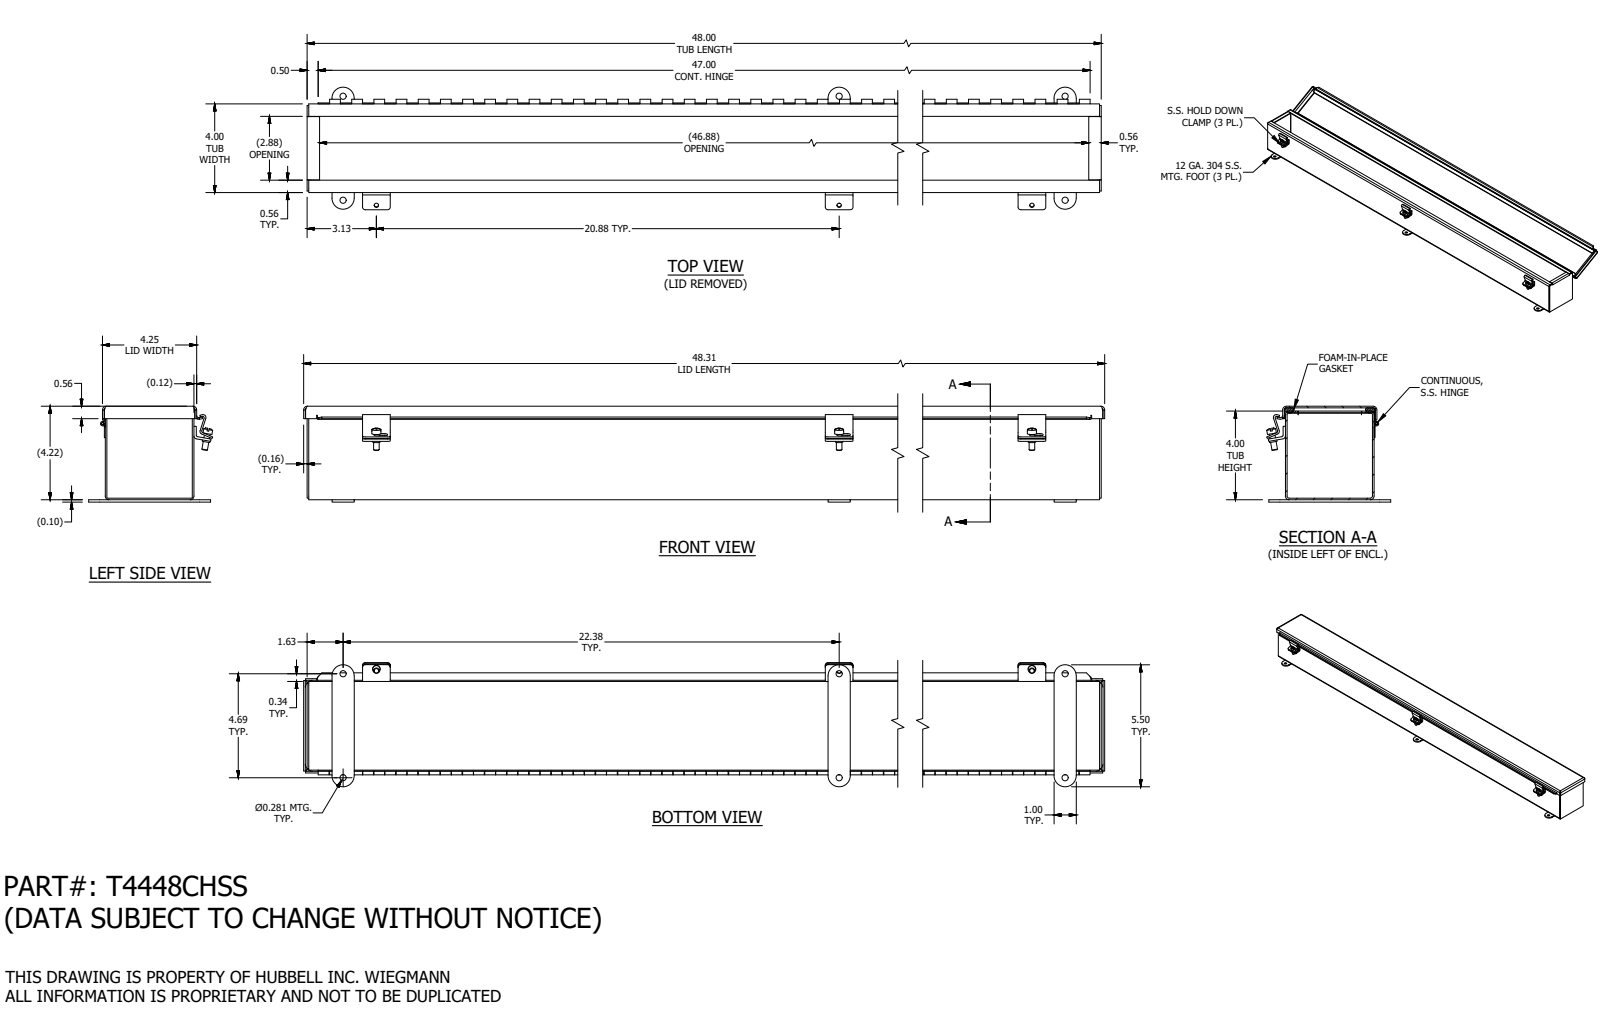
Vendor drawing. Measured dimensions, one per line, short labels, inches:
name: T4448CHSS
written by: SolidWorks 2019 (AUTOMOTIVE_DESIGN)
unit: in
bodies: 20 solids, 839 faces (503 planar, 297 cylindrical, 39 other)
size: 48.313 × 5.598 × 4.322
volume: 81.54 in³; area: 2 169 in²
holes: 6× ⌀0.11, 6× ⌀0.281, 3× ⌀0.196, 1× ⌀0.116
bosses: 3× ⌀0.41, 3× ⌀0.344, 3× ⌀0.25, 1× ⌀0.2, 1× ⌀0.1
rounds: 12× R0.125, 11× R0.094, 11× R0.168, 8× R0.085, 6× R0.133, 6× R0.5, 4× R0.242, 3× R0.063
face distances: 0.074, 3.926, 4.144, 4, 3.852, 4.218, 4.07, 0.218, 4.052, 0.126
hole spacings: 20.875, 22.375, 22.861, 0.75, 4.687, 20.875, 41.75, 44.75
